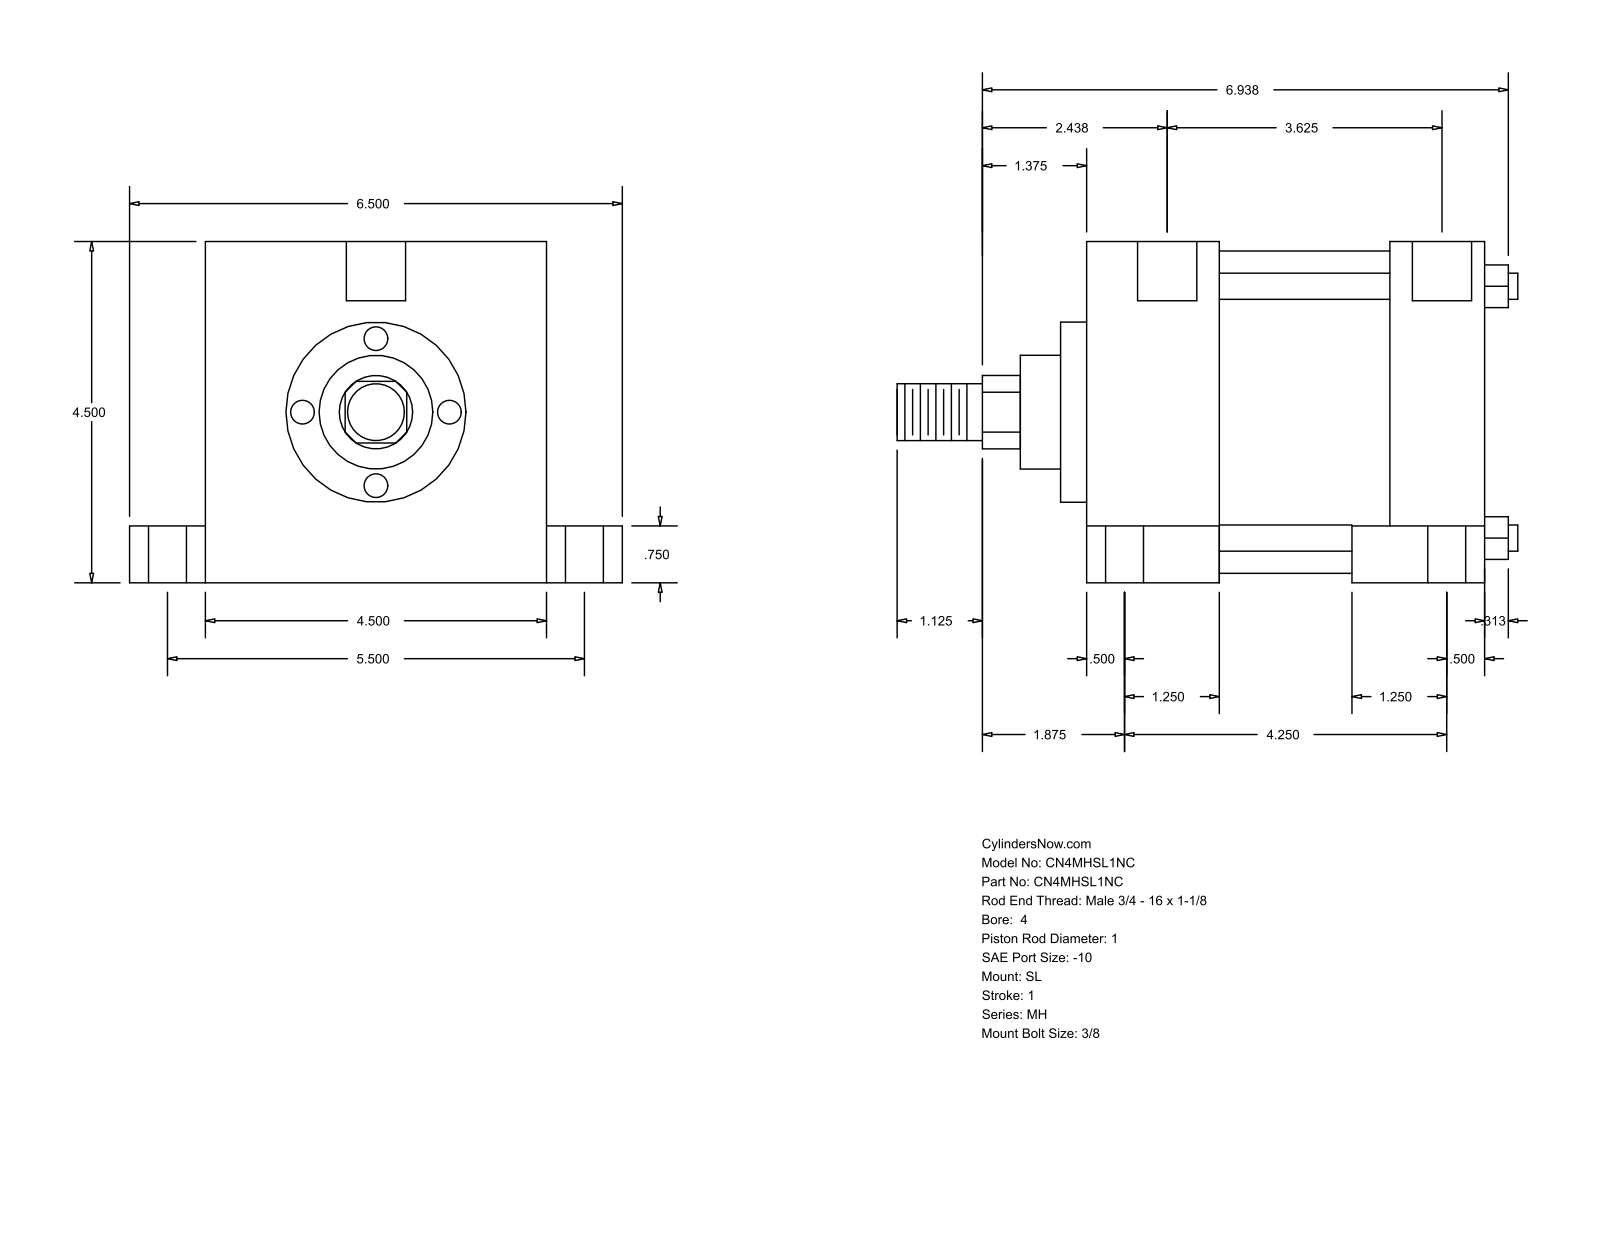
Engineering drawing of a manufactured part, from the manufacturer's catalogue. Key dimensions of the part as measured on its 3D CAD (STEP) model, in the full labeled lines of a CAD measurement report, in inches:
Part name (STEP PRODUCT): MH_SL__0400_1
STEP written by: GSSL Pune (CONFIG_CONTROL_DESIGN)
Units: inches
Bodies: 0 solids, 110 faces (77 planar, 33 cylindrical, 0 other)
Overall size (bounding box): 8.187 × 6.5 × 4.5
Round holes (diameter × count): ⌀0.344 ×4, ⌀0.5 ×4, ⌀0.75 ×4, ⌀0.781 ×2
Round bosses / shafts (diameter × count): ⌀0.345 ×4, ⌀4.25 ×1, ⌀2.375 ×1, ⌀1.5 ×1, ⌀1 ×1, ⌀0.75 ×1
Partial cylindrical surfaces — rounded edges, fillets, slot ends (radius × count): R0.484 ×1
Main face-to-face distances: 4.5, 5.25, 1.75, 3.5, 4, 2.25, 1.25, 1, 5.5, 0.75
Hole centre spacings: 0.062, 2.75, 2.751, 2.795, 2.807, 3.687, 3.75, 4.25
